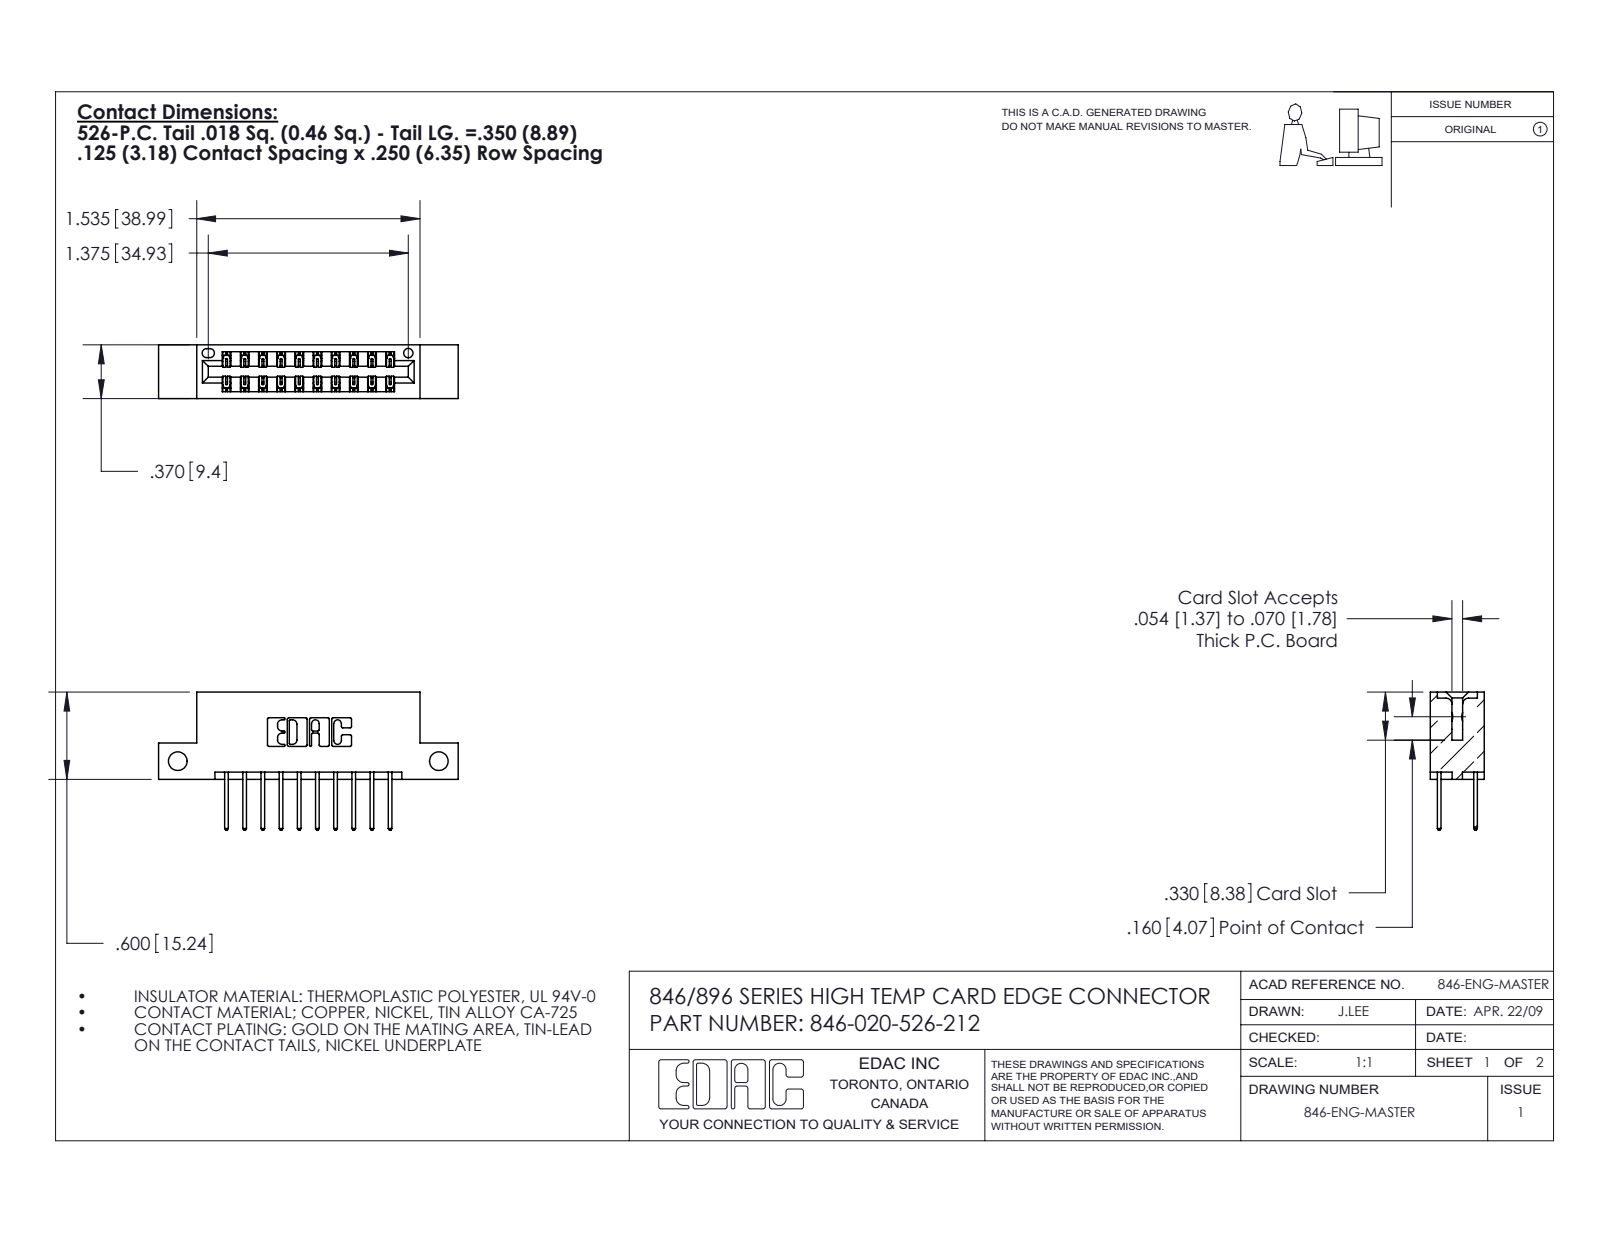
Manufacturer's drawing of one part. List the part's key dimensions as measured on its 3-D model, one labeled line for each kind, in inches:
Part name (STEP PRODUCT): 346 Part_Flush Mounting Lugs - Side Mount; 345-292-001_345-293-126; 346-020-526-212
STEP written by: SolidWorks 2016 (CONFIG_CONTROL_DESIGN)
Units: inches
Bodies: 12 solids, 748 faces (506 planar, 242 cylindrical, 0 other)
Overall size (bounding box): 2.06 × 0.95 × 0.37
Volume: 0.287 in³ · Surface area: 8.43 in²
Round holes (diameter × count): ⌀0.128 ×2, ⌀0.064 ×1
Partial cylindrical surfaces — rounded edges, fillets, slot ends (radius × count): R0.01 ×22, R0.006 ×21, R0.01 ×20, R0.007 ×6, R0.031 ×6, R0.026 ×3, R0.014 ×2, R0.022 ×2
Main face-to-face distances: 0.25, 0.048, 0.322, 0.37, 0.072, 0.298, 0.025, 0.148, 0.222, 0.1
Hole centre spacings: 1.795
